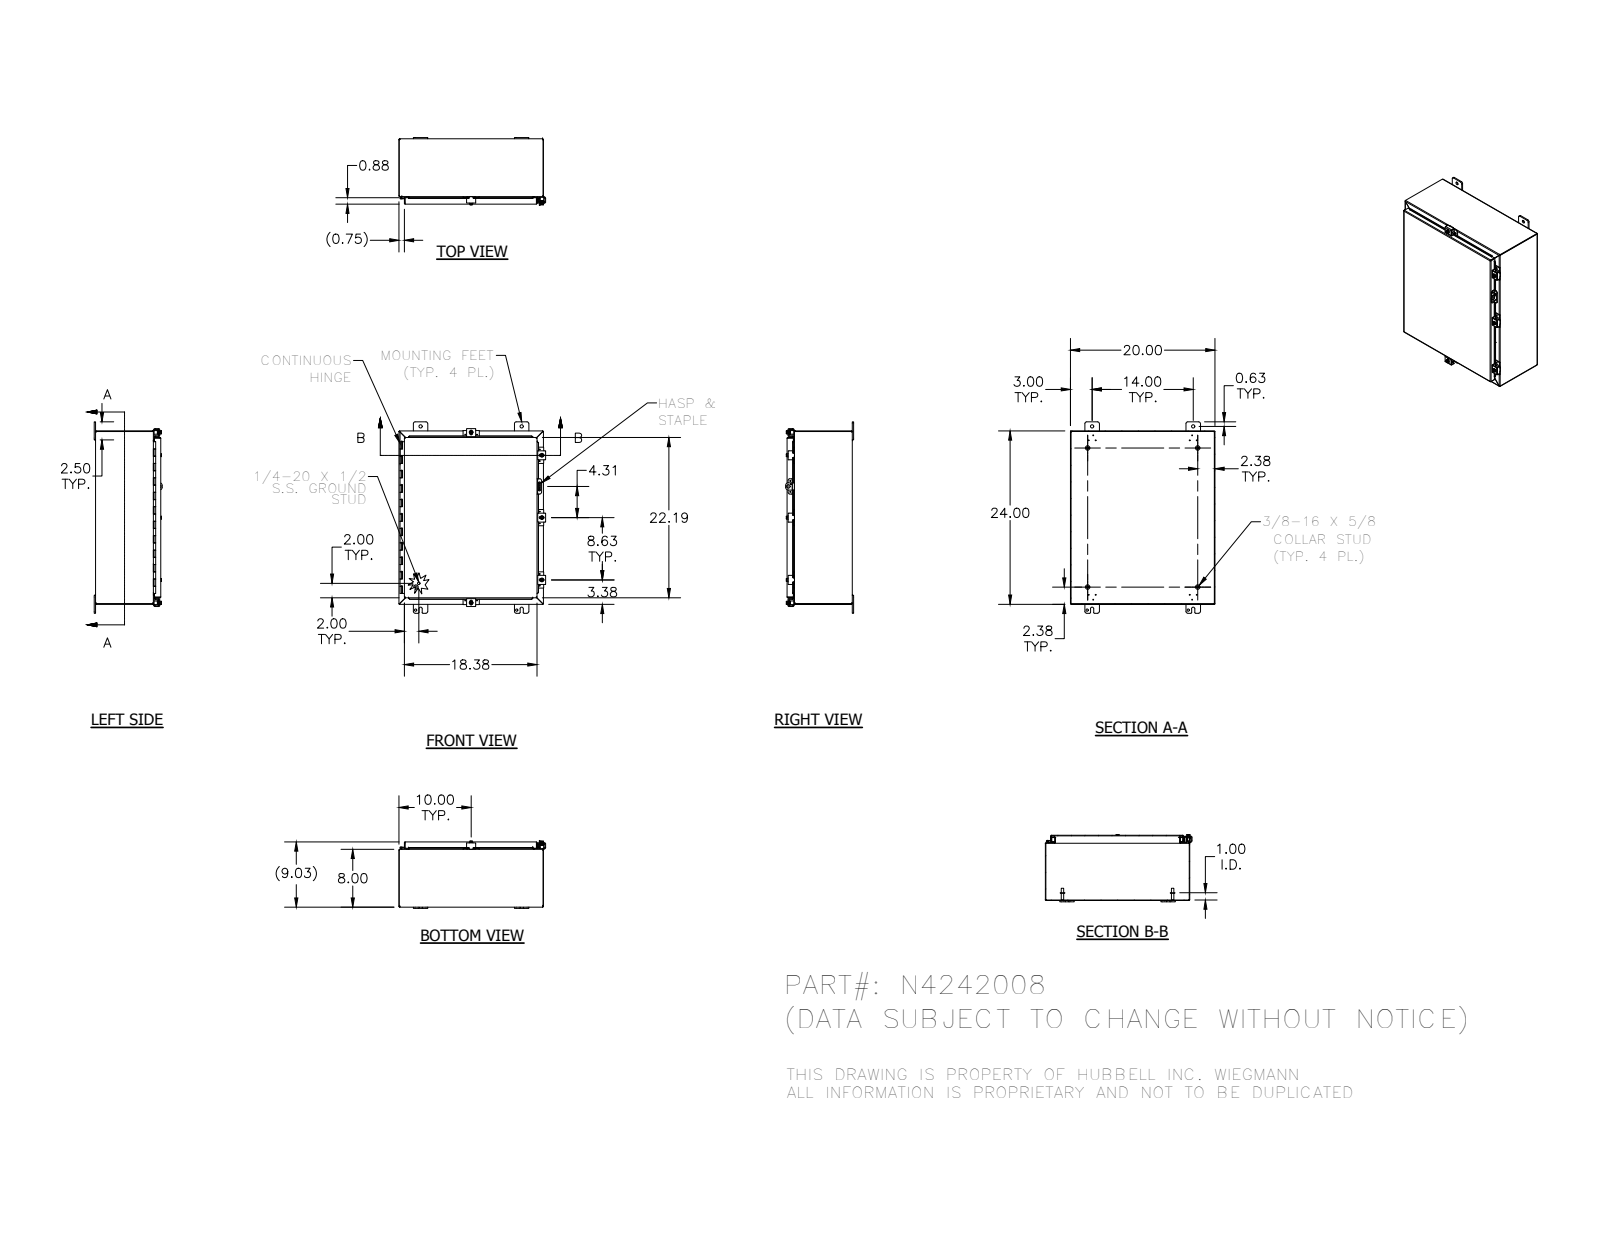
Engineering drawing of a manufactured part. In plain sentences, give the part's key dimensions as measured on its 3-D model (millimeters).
The part is named "N4242008; 30817_1; 38846_1; 38420_1 (+8 more)". Its 3-D file was written by "SolidWorks 2014 (AUTOMOTIVE_DESIGN)". It is 42 solids with 1854 faces: 722 planar, 833 cylindrical and 299 other. Overall it measures 673.1 by 515.9 by 239 millimeters. Its volume is 2 525 000 cubic millimeters and its surface area 2 593 000 square millimeters. Round holes: 13 of diameter 2.8, 12 of diameter 3, 5 of diameter 5.4, 5 of diameter 7.1, 5 of diameter 7.6, 4 of diameter 8, 4 of diameter 11.1, 1 of diameter 3.2, 1 of diameter 4, 1 of diameter 12.7. Round bosses or shafts: 7 of diameter 6.4, 5 of diameter 13.2, 5 of diameter 12.7, 5 of diameter 8.9, 4 of diameter 15.9, 4 of diameter 8.4, 2 of diameter 2.9, 1 of diameter 8.6. Partial cylindrical surfaces (rounded edges, fillets, slot ends): 61 of radius 0.8, 37 of radius 1.6, 35 of radius 3.2, 31 of radius 6.4, 23 of radius 0.8, 23 of radius 2.7, 10 of radius 3.6, 8 of radius 1.6. The main face-to-face distances are 1.9, 227.6, 225.7, 229.4, 506.1, 607.7, 201.3, 26.2, 504.2, 508. The hole center spacings are 355.6, 22.3, 19.3, 21.3, 23.9, 24.6, 40.5, 50.7.
